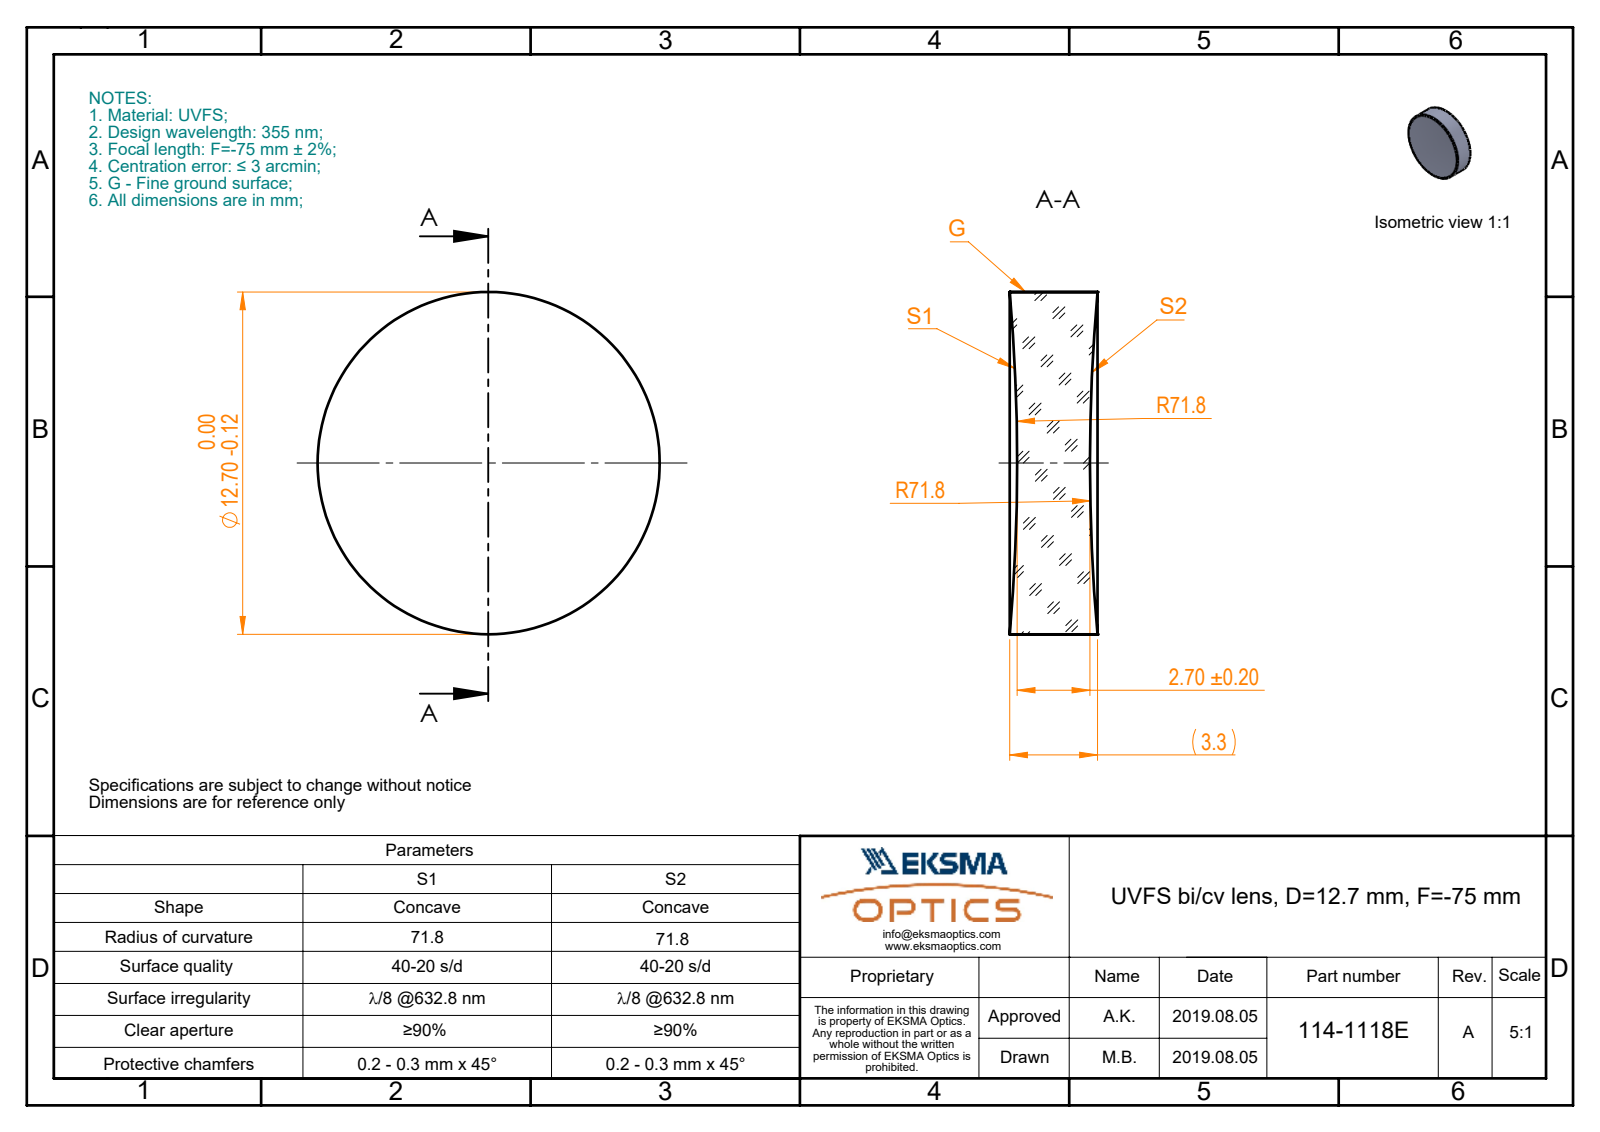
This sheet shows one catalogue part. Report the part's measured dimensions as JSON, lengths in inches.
{"part_name": "114-1118E UVFS bi-cv 12.7 F-75", "step_written_by": "SolidWorks 2017 (CONFIG_CONTROL_DESIGN)", "units": "inches", "bodies": {"solids": 1, "faces": 6, "planar": 0, "cylindrical": 2, "other": 4}, "overall_size": [0.5, 0.5, 0.128], "volume_in3": 0.023, "surface_area_in2": 0.595, "round_bosses_or_shafts": [[0.5, 1]]}
